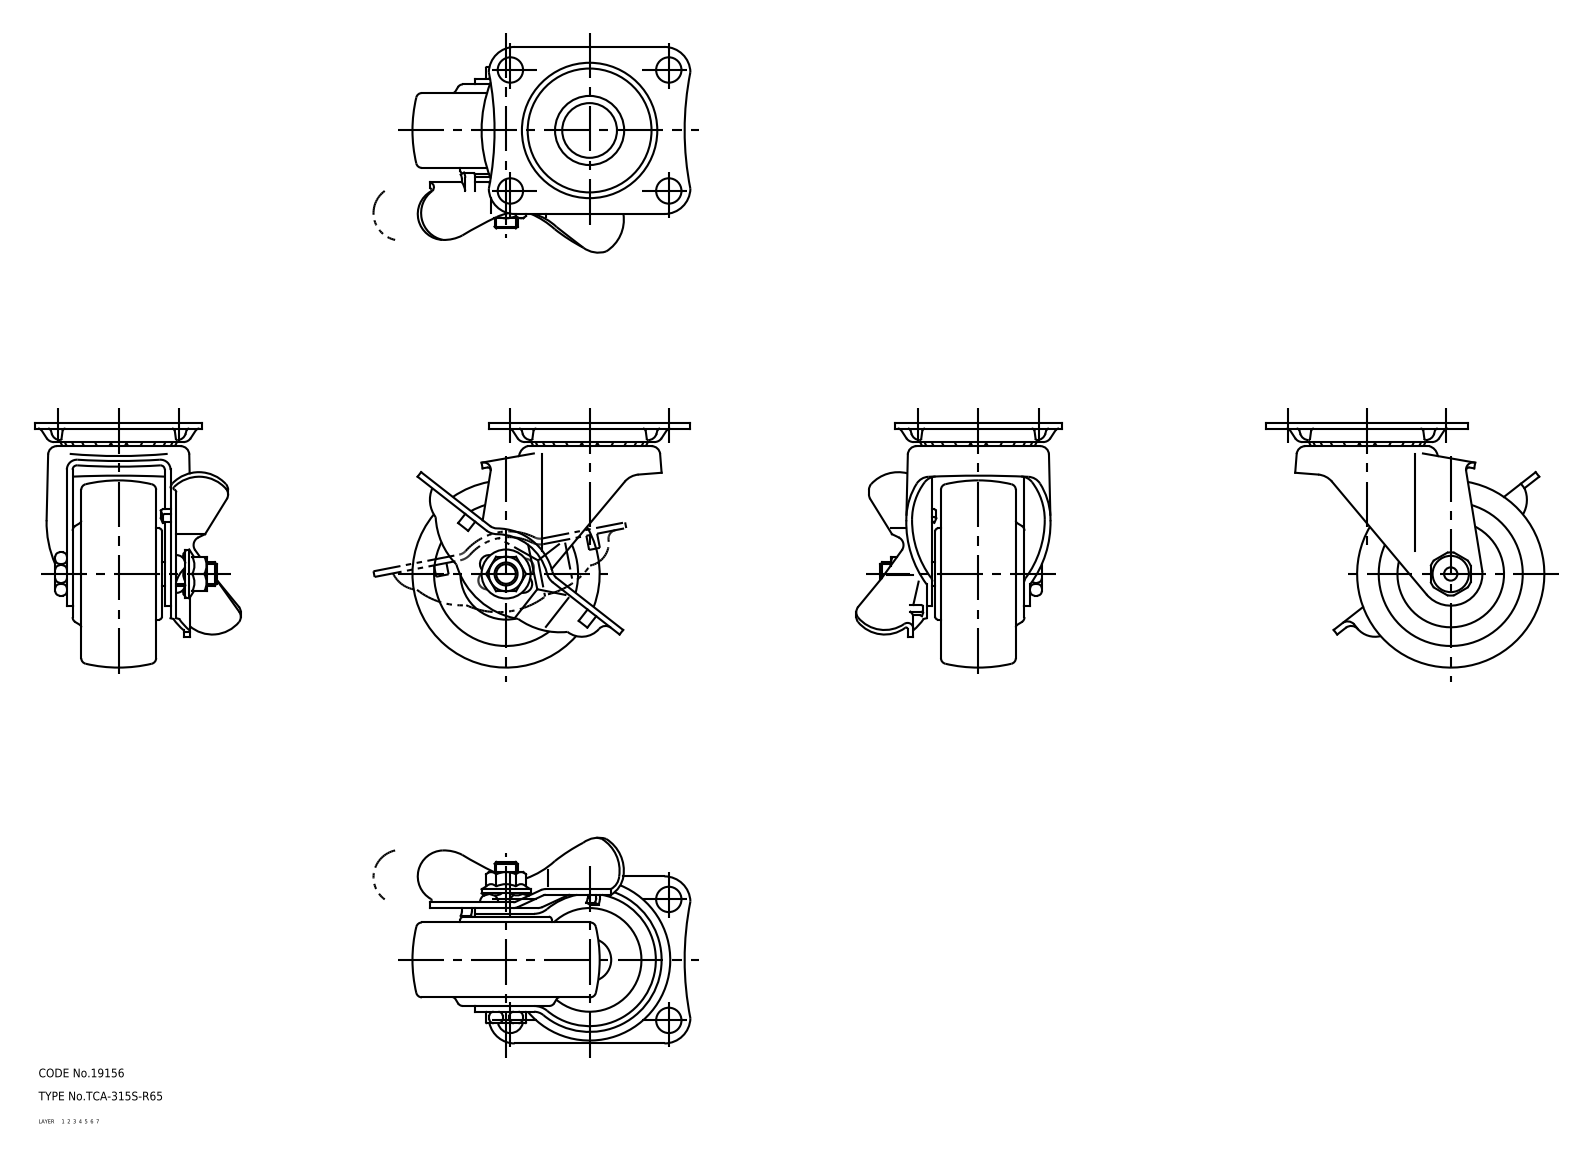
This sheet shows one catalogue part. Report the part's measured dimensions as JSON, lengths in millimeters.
{"part_name": "wheel; mounting plate; main shaft; lever (+2 more)", "step_written_by": "CADfix (AUTOMOTIVE_DESIGN)", "units": "millimeters", "bodies": {"solids": 6, "faces": 501, "planar": 0, "cylindrical": 0, "other": 501}, "overall_size": [96.5, 85, 71.4], "volume_mm3": 123943, "surface_area_mm2": 46364}
